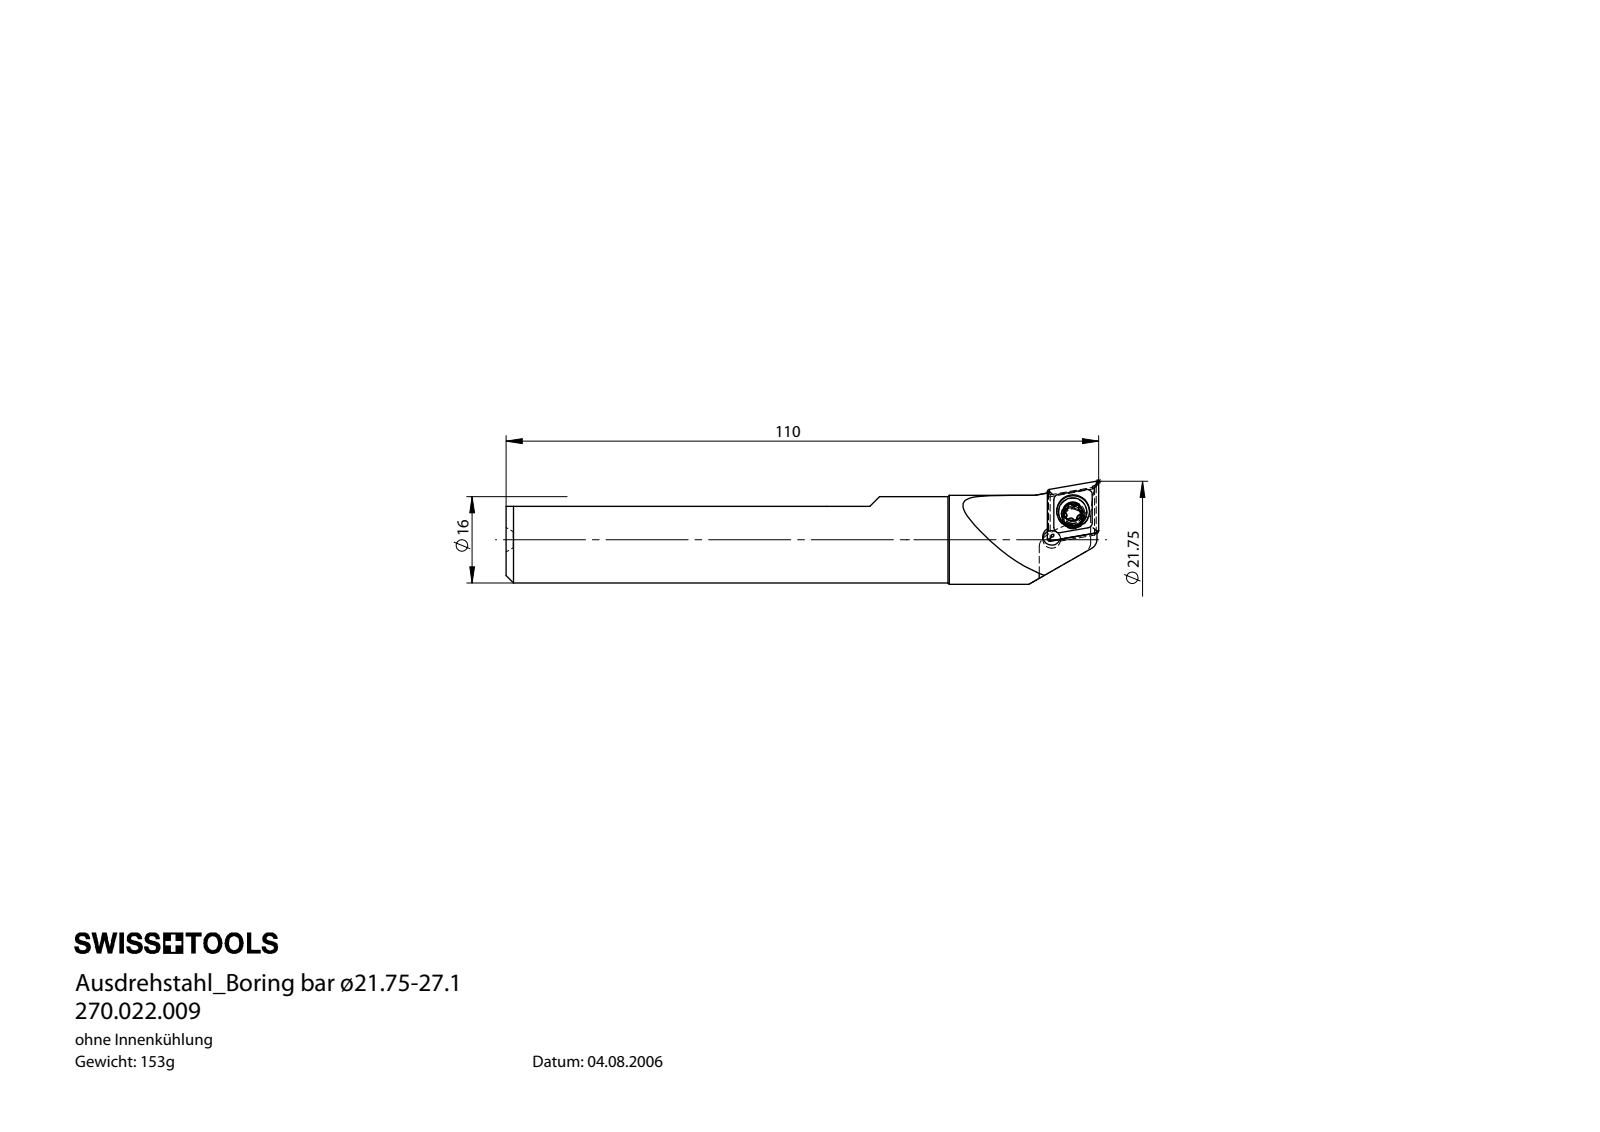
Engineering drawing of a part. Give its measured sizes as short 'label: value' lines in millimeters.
name: 270.022.009; CCMT09T304; B22-WCB.001.110_A; WCB-ER2.001.009_A
written by: SolidWorks 2022 (AUTOMOTIVE_DESIGN)
unit: mm
bodies: 3 solids, 124 faces (32 planar, 35 cylindrical, 57 other)
size: 110 × 19.12 × 17.34
volume: 19 883 mm³; area: 6 193 mm²
holes: 2× ⌀3.3, 1× ⌀4.4, 1× ⌀6.1
bosses: 1× ⌀16.5, 1× ⌀16, 1× ⌀5.25, 1× ⌀4
rounds: 6× R0.34, 6× R0.59, 1× R2, 1× R8.4, 1× R12
face distances: 5.94, 9.71, 3.77, 9.91, 3.97, 100.66, 0.92, 5.02, 8.79, 8.99
hole spacings: 6.07, 6.19
